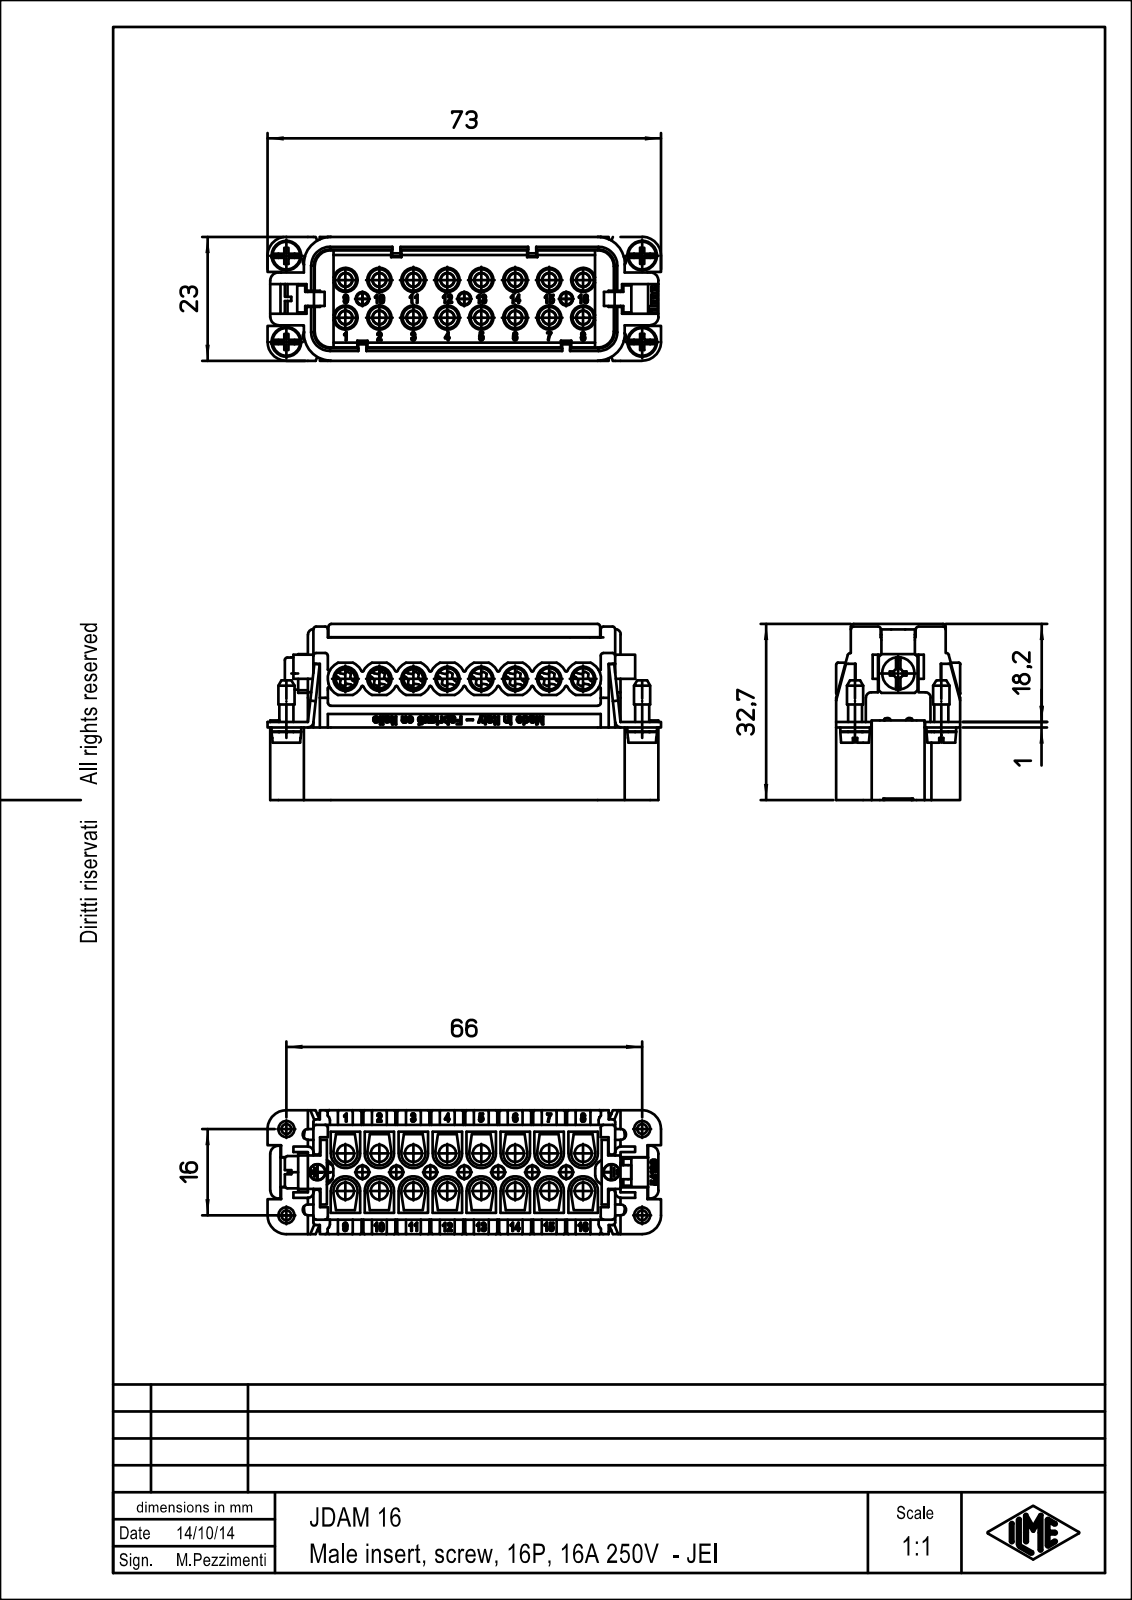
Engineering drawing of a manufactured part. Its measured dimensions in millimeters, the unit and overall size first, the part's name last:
Units: millimetres
Overall size (bounding box): 73 × 32.2 × 23
Round holes (diameter × count): ⌀3.2 ×16, ⌀4.1 ×8, ⌀3 ×4, ⌀1.8 ×1
Round bosses / shafts (diameter × count): ⌀2.5 ×16, ⌀3 ×8, ⌀5.5 ×4, ⌀2.6 ×4, ⌀6 ×1, ⌀4.5 ×1, ⌀3.5 ×1
Partial cylindrical surfaces — rounded edges, fillets, slot ends (radius × count): R0.5 ×57, R0.3 ×32, R1 ×20, R2.25 ×16, R0.2 ×11, R1.5 ×8, R3.3 ×8, R2 ×4
Main face-to-face distances: 23, 1, 2, 2.7, 13.7, 20.3, 2.15, 6.3, 13.5, 5.5
Hole centre spacings: 6.3, 12.6, 18.9, 9.42, 14.41, 25.2, 20.15, 31.5
Volume: 21 780 mm³ · Surface area: 21 054 mm²
Bodies: 1 solid, 2037 faces (1025 planar, 537 cylindrical, 475 other)
Part name (STEP PRODUCT): JDAM_16
STEP written by: PTC Creo Elements/Direct Modeling 19.0B 21-Mar-2015 (C) Parametric Technology GmbH (AUTOMOTIVE_DESIGN)
